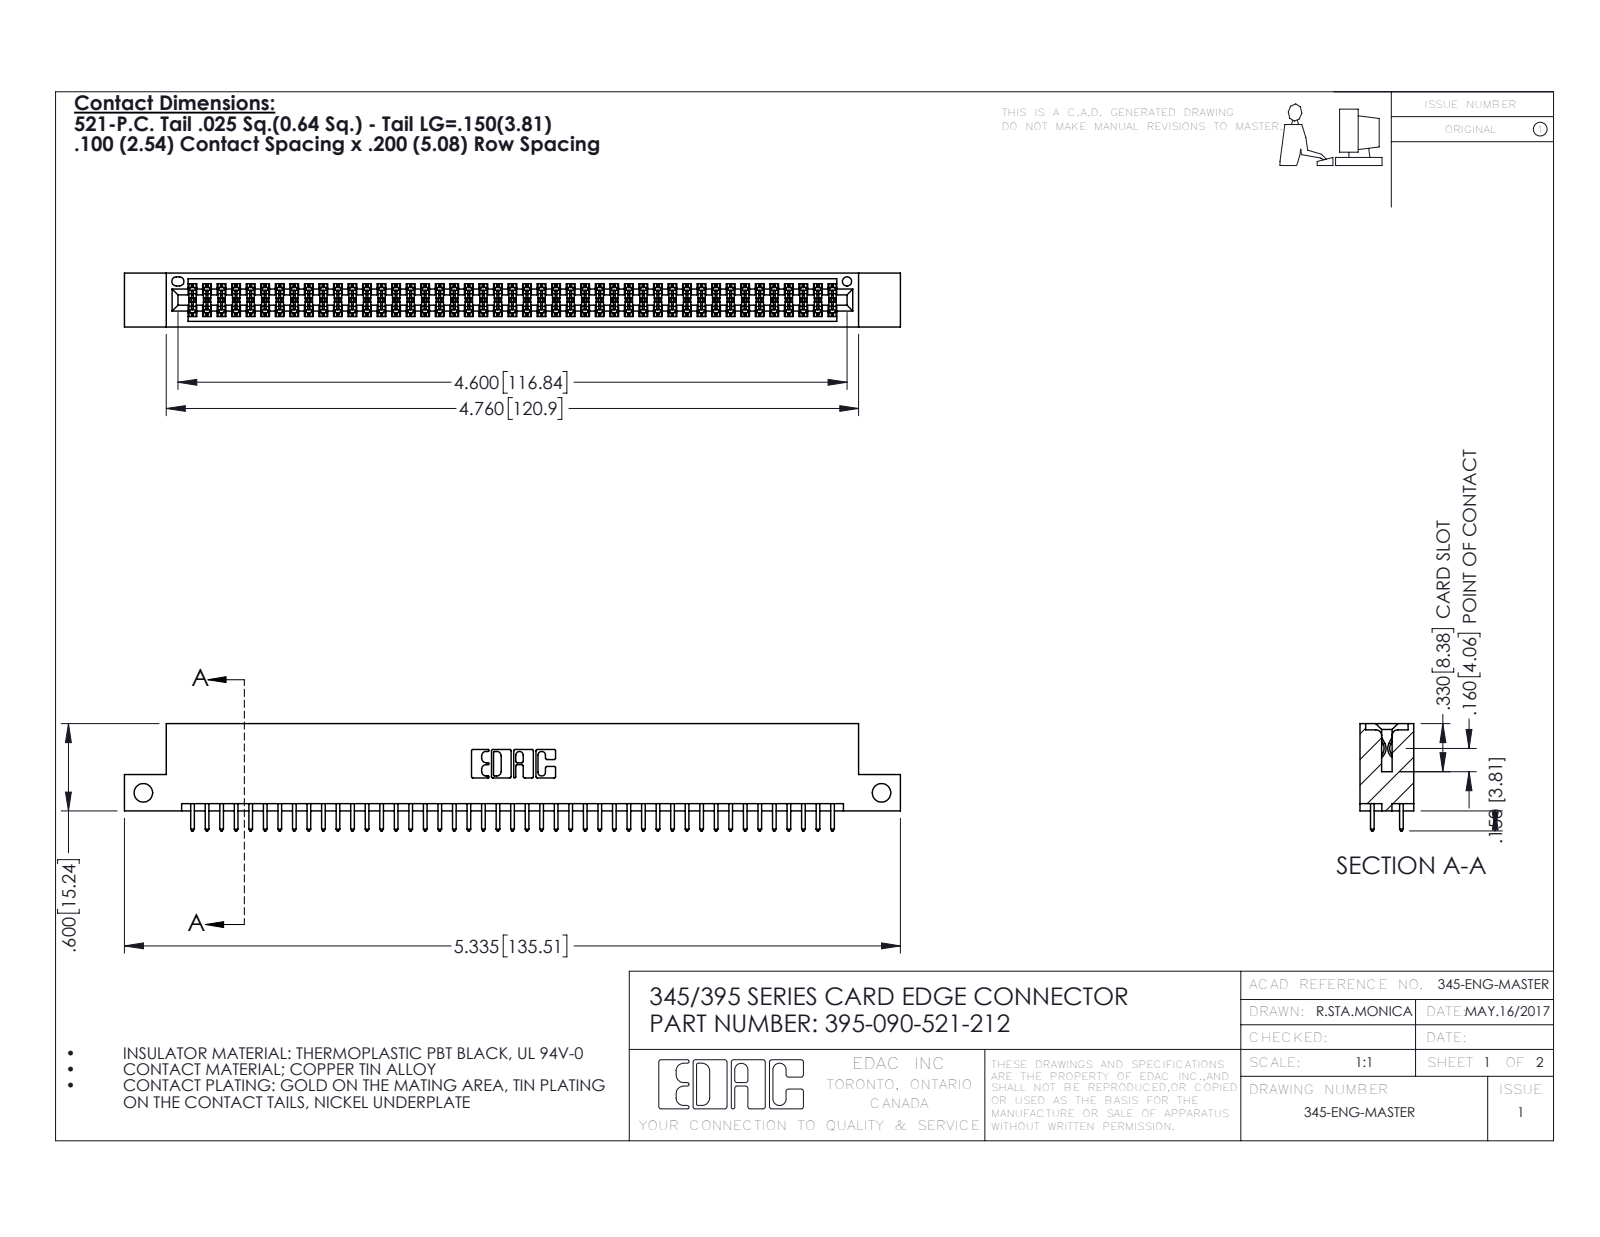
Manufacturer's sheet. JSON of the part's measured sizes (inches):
{"part_name": "345 Part_Flush Mounting Lugs - Side Mount; 345-292-001_345-293-121; 395-090-521-212", "step_written_by": "SolidWorks 2016 (CONFIG_CONTROL_DESIGN)", "units": "inches", "bodies": {"solids": 91, "faces": 4626, "planar": 3050, "cylindrical": 1576, "other": 0}, "overall_size": [5.335, 0.737, 0.37], "volume_in3": 0.797, "surface_area_in2": 29.45, "round_holes": [[0.128, 2], [0.064, 1]], "partial_cylinders_radius": [[0.006, 135], [0.01, 90], [0.01, 22], [0.007, 6], [0.031, 6], [0.026, 3], [0.014, 2], [0.019, 2]], "face_to_face_distances": [0.298, 0.072, 0.2, 0.37, 0.098, 0.272, 0.025, 0.225, 0.175, 0.149], "hole_center_spacings": [5.075]}
